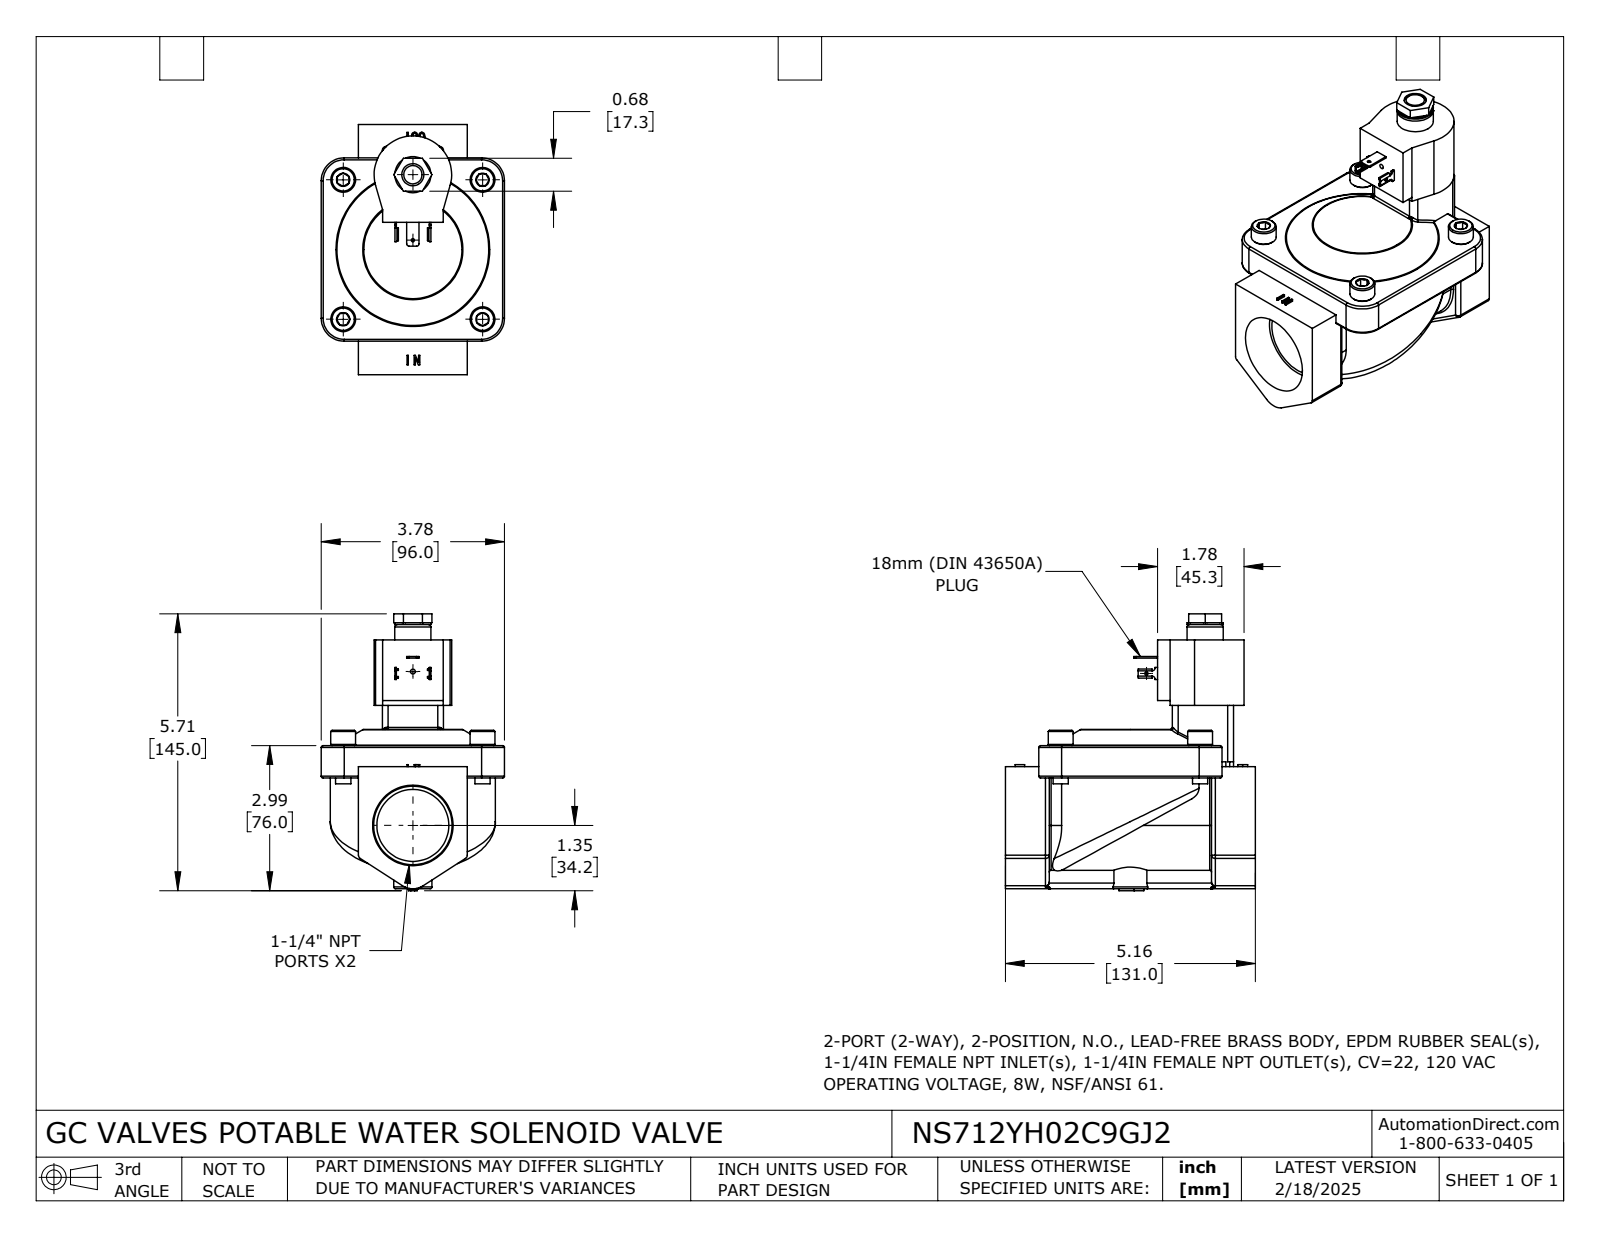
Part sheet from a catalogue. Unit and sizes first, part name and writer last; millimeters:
Units: millimetres
Overall size (bounding box): 145.01 × 131 × 96
Round holes (diameter × count): ⌀1.68 ×1, ⌀1.7 ×1, ⌀2.53 ×1, ⌀11.58 ×1, ⌀30.48 ×1, ⌀37.69 ×1
Round bosses / shafts (diameter × count): ⌀13 ×4, ⌀8 ×4, ⌀18.95 ×1
Partial cylindrical surfaces — rounded edges, fillets, slot ends (radius × count): R2 ×14, R1 ×13, R3 ×6, R0.15 ×4, R1.04 ×4, R12 ×4, R0.2 ×2, R1.27 ×2
Main face-to-face distances: 19.5, 11, 32, 6, 76.5, 8.5, 96, 17, 25.5, 57
Hole centre spacings: 34.29, 80.56
Volume: 569 084 mm³ · Surface area: 70 720 mm²
Bodies: 1 solid, 456 faces (206 planar, 120 cylindrical, 130 other)
Part name (STEP PRODUCT): NS712YH02C9GJ2
STEP written by: SolidWorks 2024 (CONFIG_CONTROL_DESIGN)
